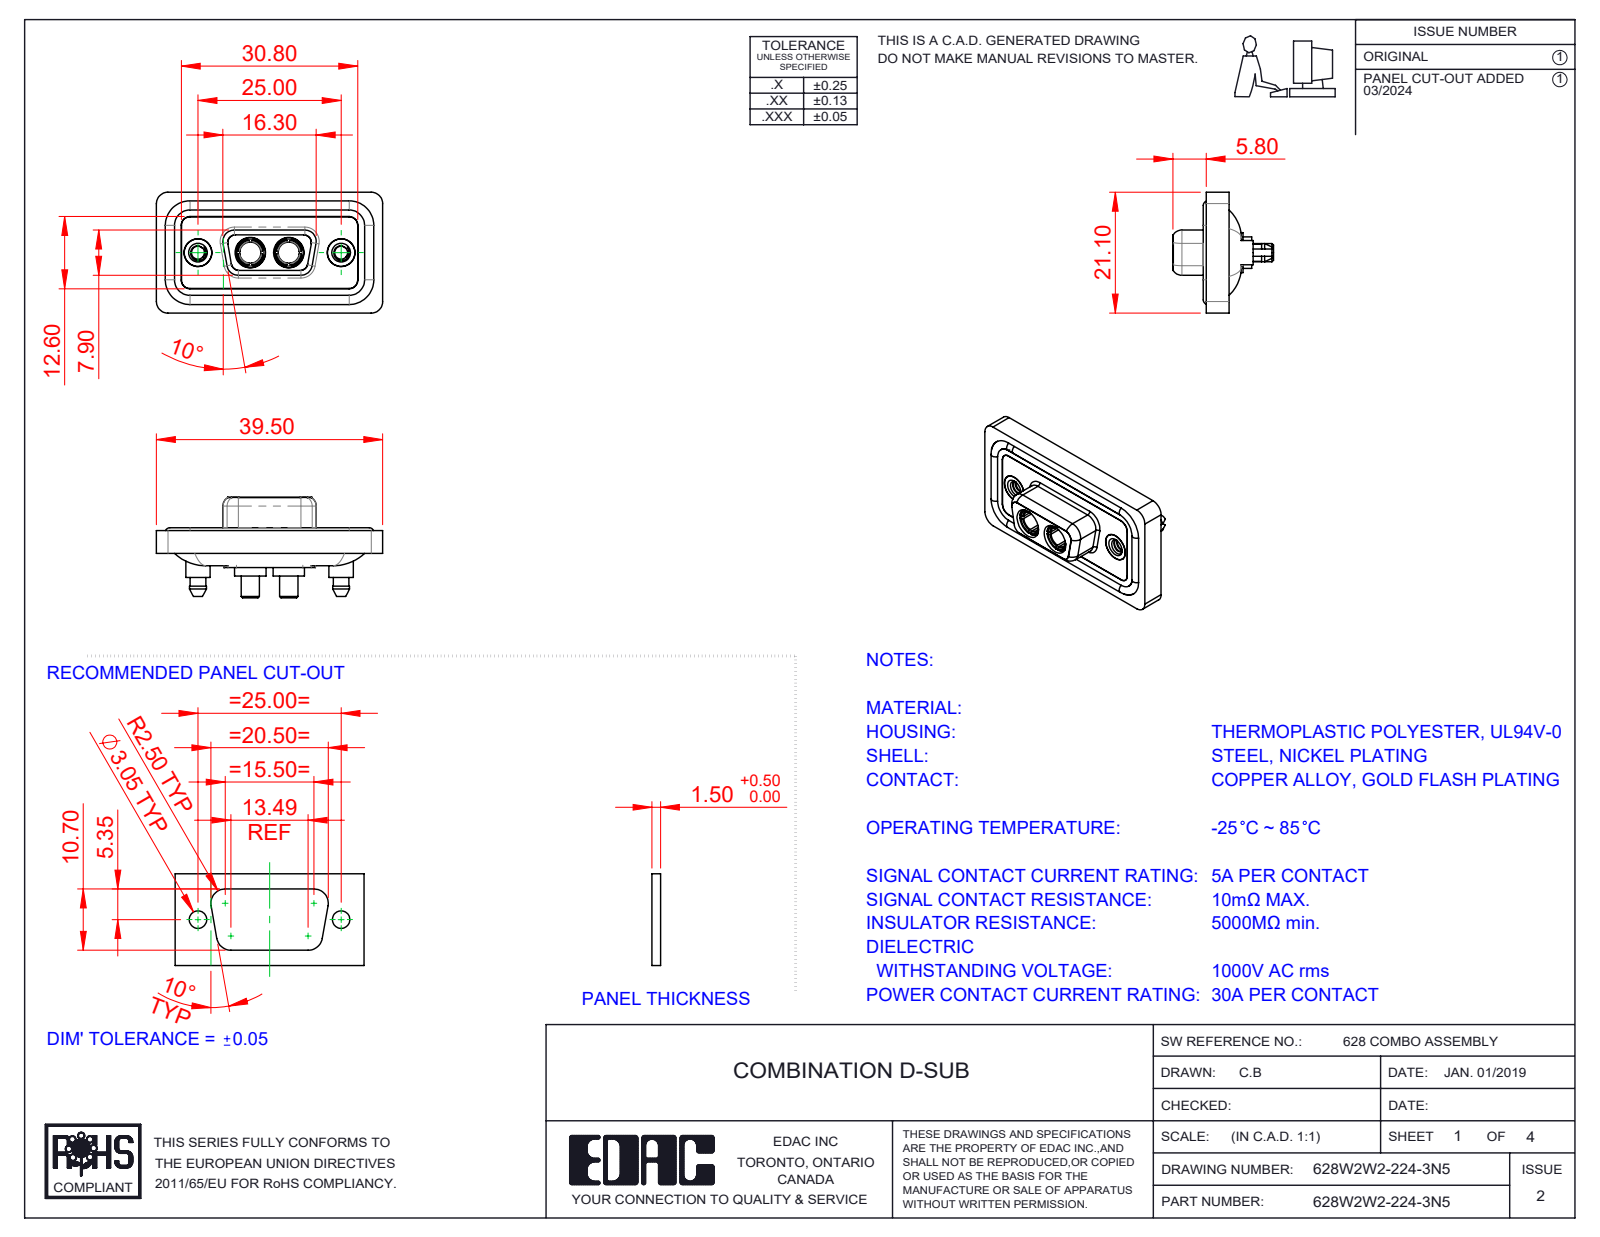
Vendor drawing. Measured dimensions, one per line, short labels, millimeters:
name: 628Combo Housing_2W2; 628Combo Waterproof Housing_09 Contacts; 628W2W2-224-3N5; 628Combo Shell Front_09 Contacts (+3 more)
written by: SolidWorks 2023 (CONFIG_CONTROL_DESIGN)
unit: mm
bodies: 11 solids, 584 faces (179 planar, 266 cylindrical, 139 other)
size: 39.5 × 21.1 × 17.55
volume: 4 861 mm³; area: 7 978 mm²
holes: 4× ⌀4.85, 2× ⌀2.26, 2× ⌀3.7, 2× ⌀4, 2× ⌀4.05, 2× ⌀5, 2× ⌀5.3
bosses: 4× ⌀1.6, 2× ⌀5.5, 2× ⌀5.4, 2× ⌀5.2, 2× ⌀4.96, 2× ⌀4.95, 2× ⌀4.8, 2× ⌀4.75
rounds: 24× R1.5, 18× R2, 10× R1.6, 8× R1.35, 4× R0.25, 4× R0.5, 4× R0.6, 4× R0.65
face distances: 0.4, 1.8, 1.1, 2.9, 1.6, 0.5, 5.65, 7.45, 1.5, 4
hole spacings: 9.14, 15.86, 6.72, 25
